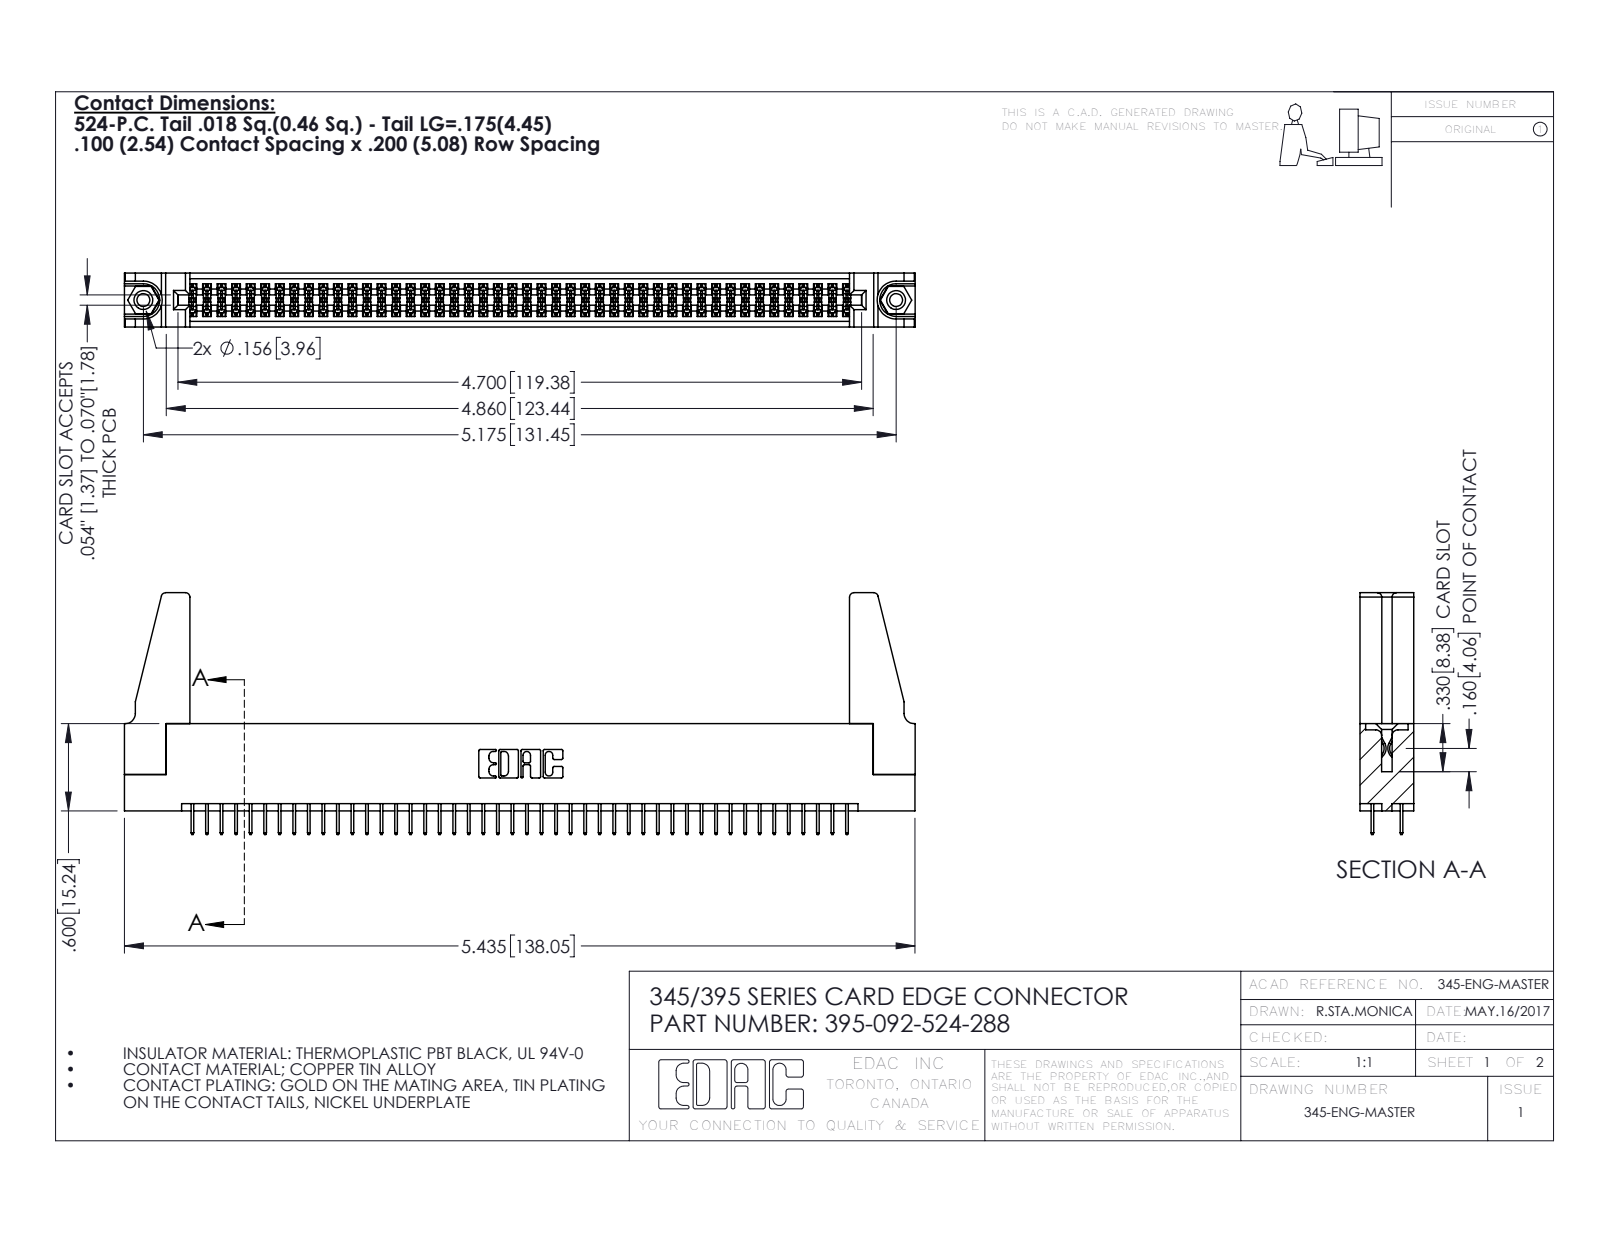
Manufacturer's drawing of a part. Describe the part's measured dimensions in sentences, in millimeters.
The part is named "395-092-524-288; 345-250-001_345-250-001-102; 345 Part_Flush Mounting Lugs - 0.156 Dia-TH; 345-292-001_345-293-124 (+1 more)". Its 3-D file was written by "SolidWorks 2016 (CONFIG_CONTROL_DESIGN)". It is 97 solids with 5218 faces: 3740 planar, 1462 cylindrical and 16 other. Overall it measures 138.1 by 42.2 by 9.4 millimeters. Its volume is 16 570 cubic millimeters and its surface area 22 510 square millimeters. Round holes: 2 of diameter 2.3, 2 of diameter 3.2, 2 of diameter 4, 1 of diameter 1.6. Round bosses or shafts: 2 of diameter 3.9. Partial cylindrical surfaces (rounded edges, fillets, slot ends): 138 of radius 0.2, 22 of radius 0.3, 8 of radius 0.8, 6 of radius 0.2, 6 of radius 0.8, 3 of radius 0.7, 2 of radius 0.4, 2 of radius 0.5. The main face-to-face distances are 1.8, 7.6, 9.4, 5.1, 2.5, 6.9, 0.6, 5.7, 1.8, 4.4. The hole center spacings are 6.9, 125.5, 131.4.
